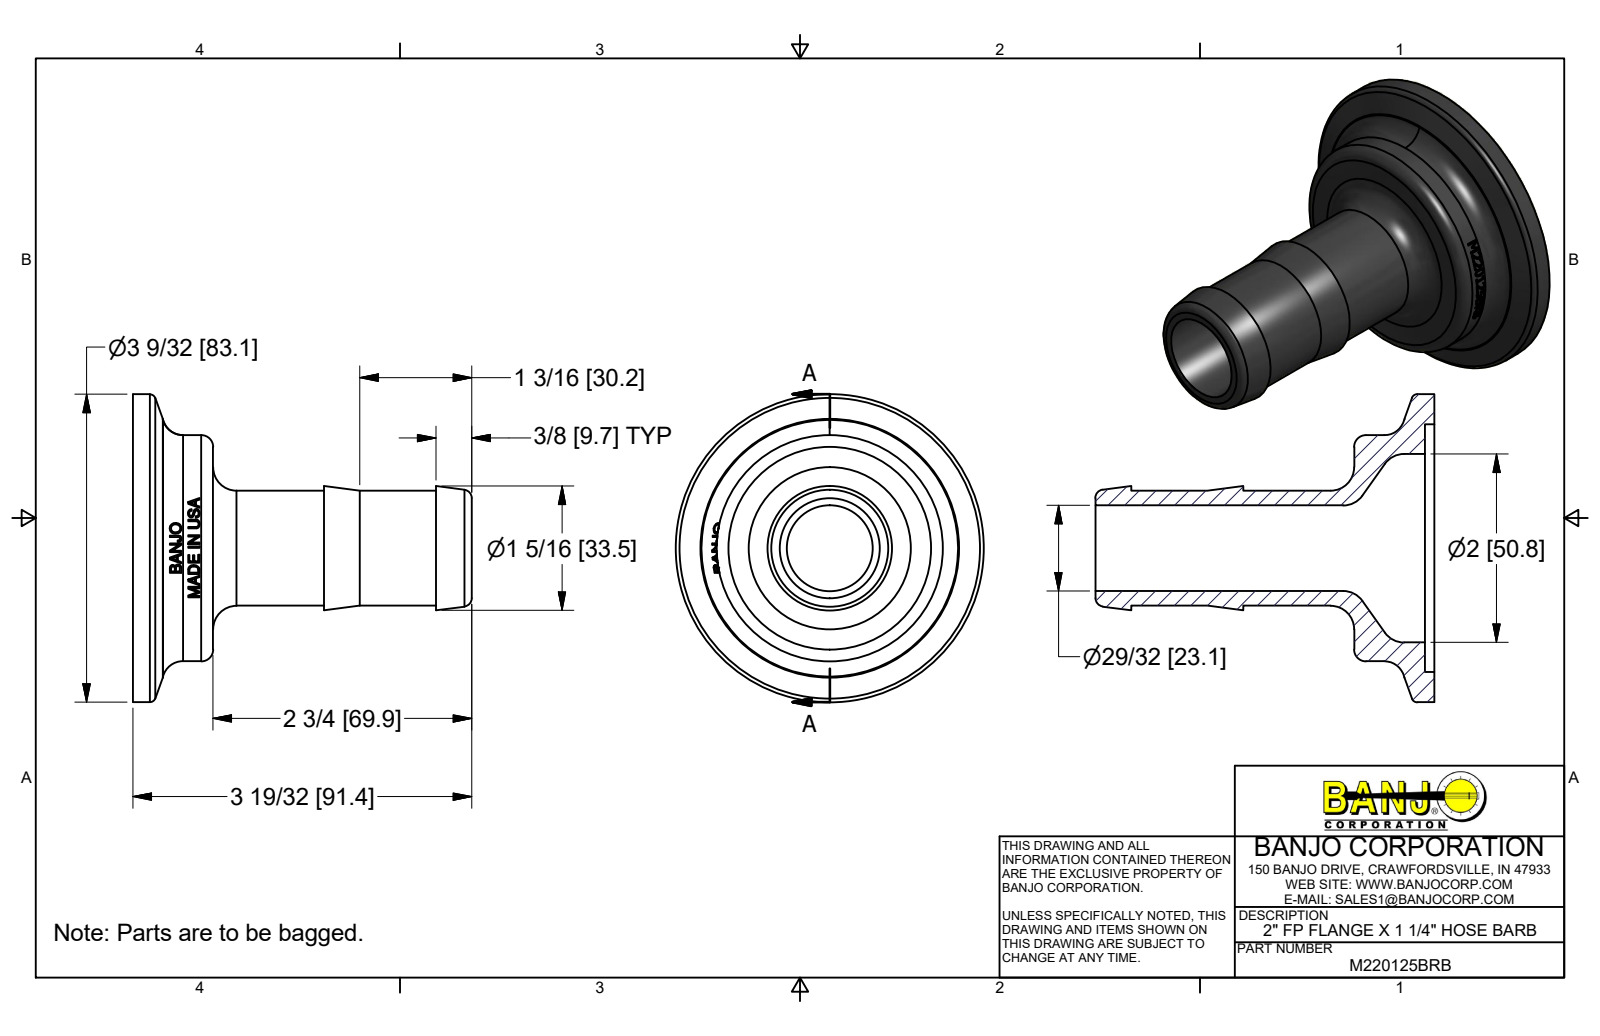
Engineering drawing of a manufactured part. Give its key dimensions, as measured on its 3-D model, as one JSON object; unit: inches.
{"part_name": "M220125BRB; M220125BRBU", "step_written_by": "Autodesk Inventor 2017 (AUTOMOTIVE_DESIGN)", "units": "inches", "bodies": {"solids": 1, "faces": 406, "planar": 198, "cylindrical": 35, "other": 173}, "overall_size": [3.6, 3.27, 3.27], "volume_in3": 4.229, "surface_area_in2": 42.98, "round_holes": [[0.91, 1], [2, 1], [2.63, 1]], "round_bosses_or_shafts": [[3.27, 1], [2.4, 1], [1.22, 1]], "partial_cylinders_radius": [[1.18, 1]], "face_to_face_distances": [0.1, 0.85, 0.75, 3.6, 3.5, 2.75, 2.03, 3.22, 1.93, 3.12]}
